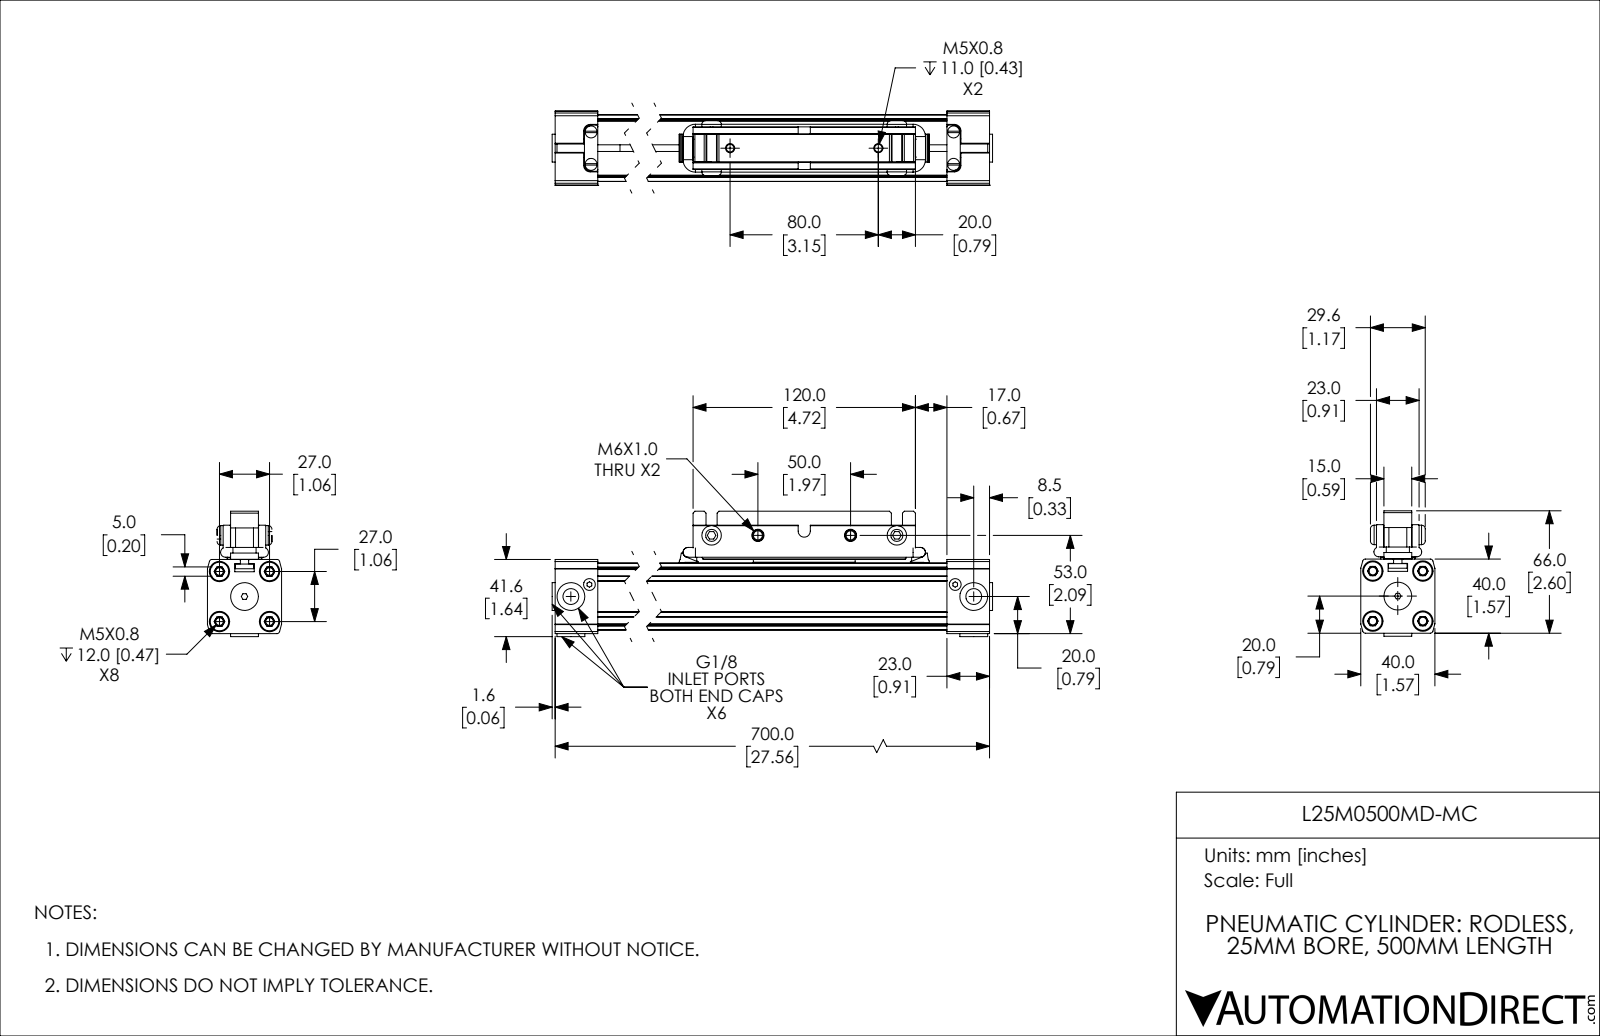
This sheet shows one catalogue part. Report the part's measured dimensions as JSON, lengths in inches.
{"part_name": "L25M0500MD-MC_BODY; L25M0500MD-MC_PISTON; L25M0500MD-MC", "step_written_by": "SolidWorks 2019 (CONFIG_CONTROL_DESIGN)", "units": "inches", "bodies": {"solids": 13, "faces": 883, "planar": 453, "cylindrical": 322, "other": 108}, "overall_size": [27.688, 2.663, 1.575], "volume_in3": 41.04, "surface_area_in2": 365.9, "round_holes": [[0.163, 6], [0.337, 5], [0.591, 5], [0.256, 4], [0.26, 4], [0.433, 4], [0.194, 2], [0.194, 2], [0.252, 2], [0.988, 1]], "round_bosses_or_shafts": [[0.394, 4], [0.383, 3], [0.323, 3], [0.413, 2], [0.21, 2], [0.21, 2], [0.984, 1]], "partial_cylinders_radius": [[0.012, 28], [0.02, 14], [0.039, 14], [0.01, 12], [0.138, 8], [0.025, 6], [0.059, 6], [0.094, 6]], "face_to_face_distances": [1.413, 1.417, 0.429, 0.635, 0.777, 0.079, 0.335, 0.906, 1.496, 0.224], "hole_center_spacings": [0.55, 0.752, 1.063, 26.463, 0.47, 0.689, 0.698, 0.809]}
